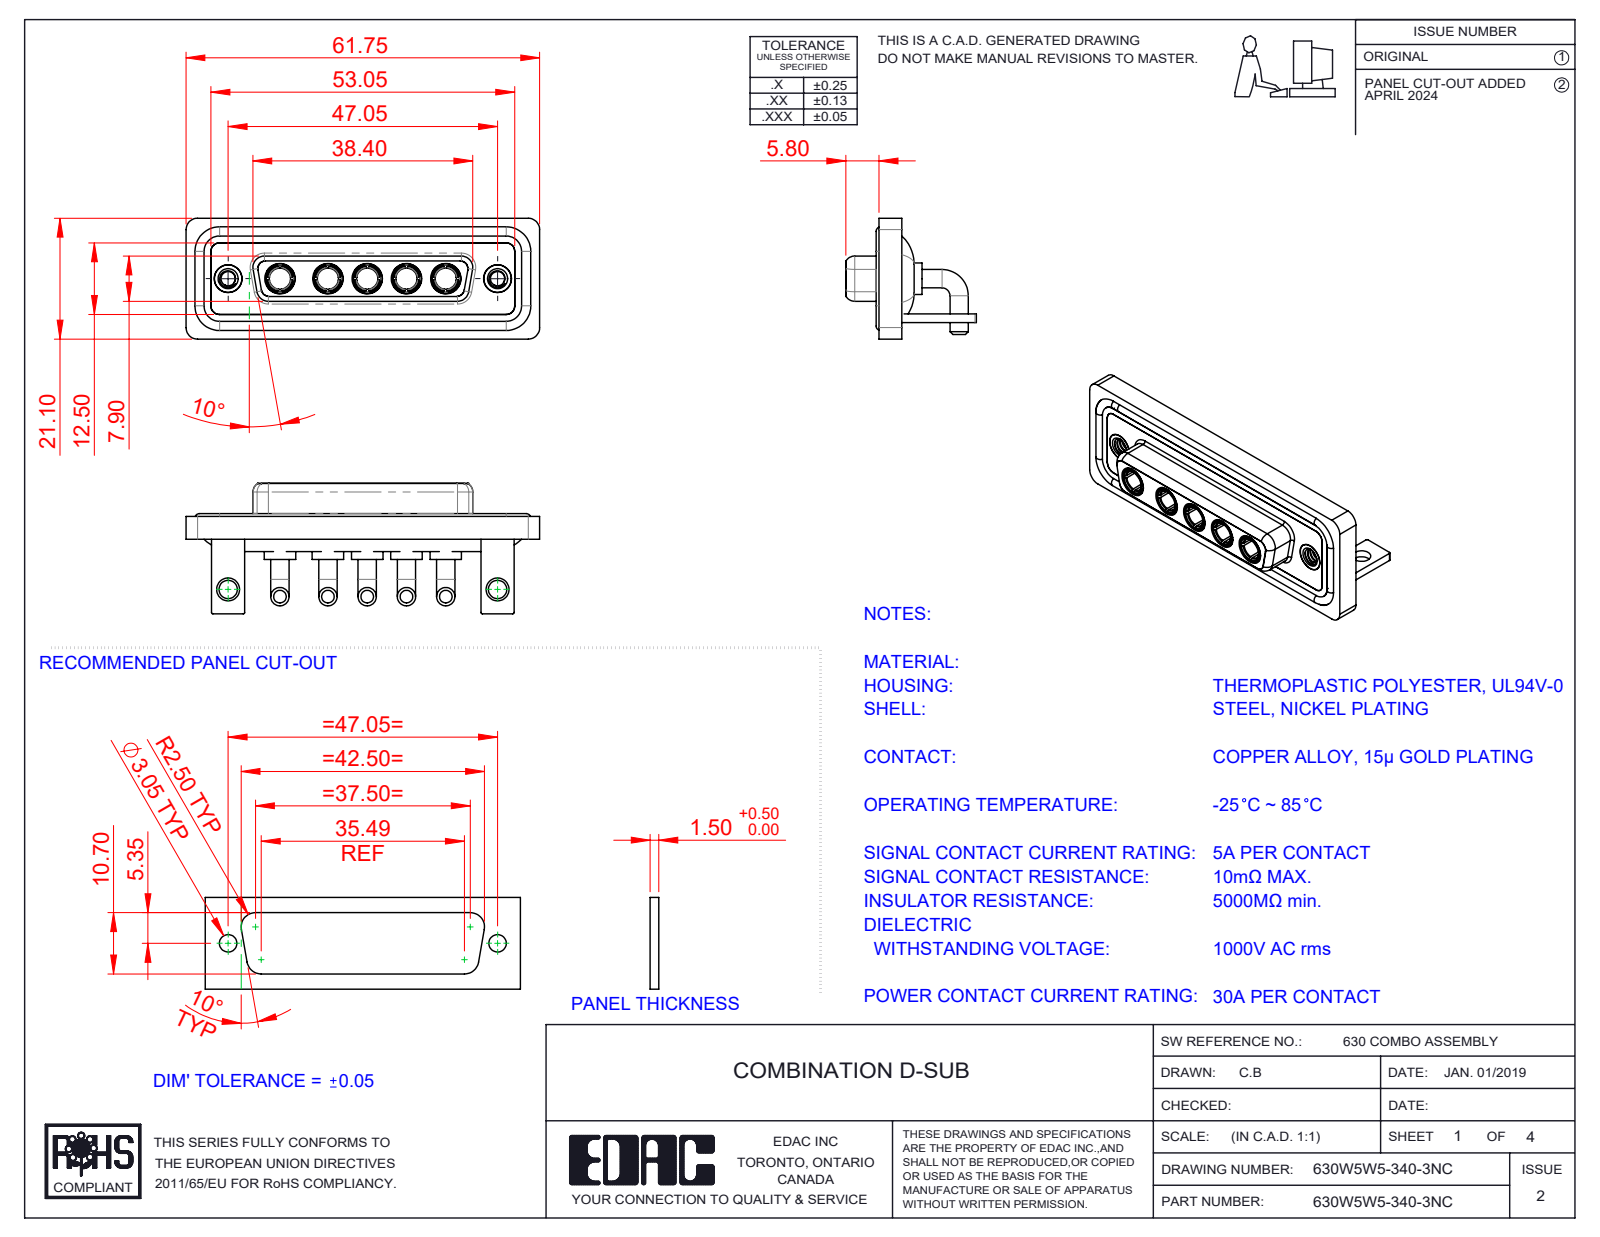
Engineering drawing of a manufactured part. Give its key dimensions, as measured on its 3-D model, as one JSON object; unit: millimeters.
{"part_name": "630Combo Waterproof Housing_25 Contacts; 630W5W5-340-3NC; 630Combo Housing_5W5; 630Combo Stabilizer Bracket_50 Contacts (+4 more)", "step_written_by": "SolidWorks 2023 (CONFIG_CONTROL_DESIGN)", "units": "millimeters", "bodies": {"solids": 19, "faces": 818, "planar": 270, "cylindrical": 335, "other": 213}, "overall_size": [61.75, 22.8, 21.1], "volume_mm3": 8934, "surface_area_mm2": 14644, "round_holes": [[4.85, 7], [3.7, 5], [5.3, 5], [2.5, 2], [3.2, 2], [4, 2], [4.05, 2], [5, 2]], "round_bosses_or_shafts": [[3.2, 10], [5.5, 5], [5.2, 5], [4.96, 5], [4.75, 5], [3.75, 5], [1.6, 4], [4.95, 2]], "partial_cylinders_radius": [[2, 19], [1.5, 18], [0.25, 16], [1.35, 8], [1.6, 8], [0.5, 5], [2.1, 5], [0.6, 4]], "face_to_face_distances": [0.4, 1.8, 2.9, 3.7, 1.5, 4.1, 1.1, 1.4, 1.6, 2.5], "hole_center_spacings": [6.86, 9.04, 38.01, 47.05, 6.87, 8.38, 13.72, 13.73]}
